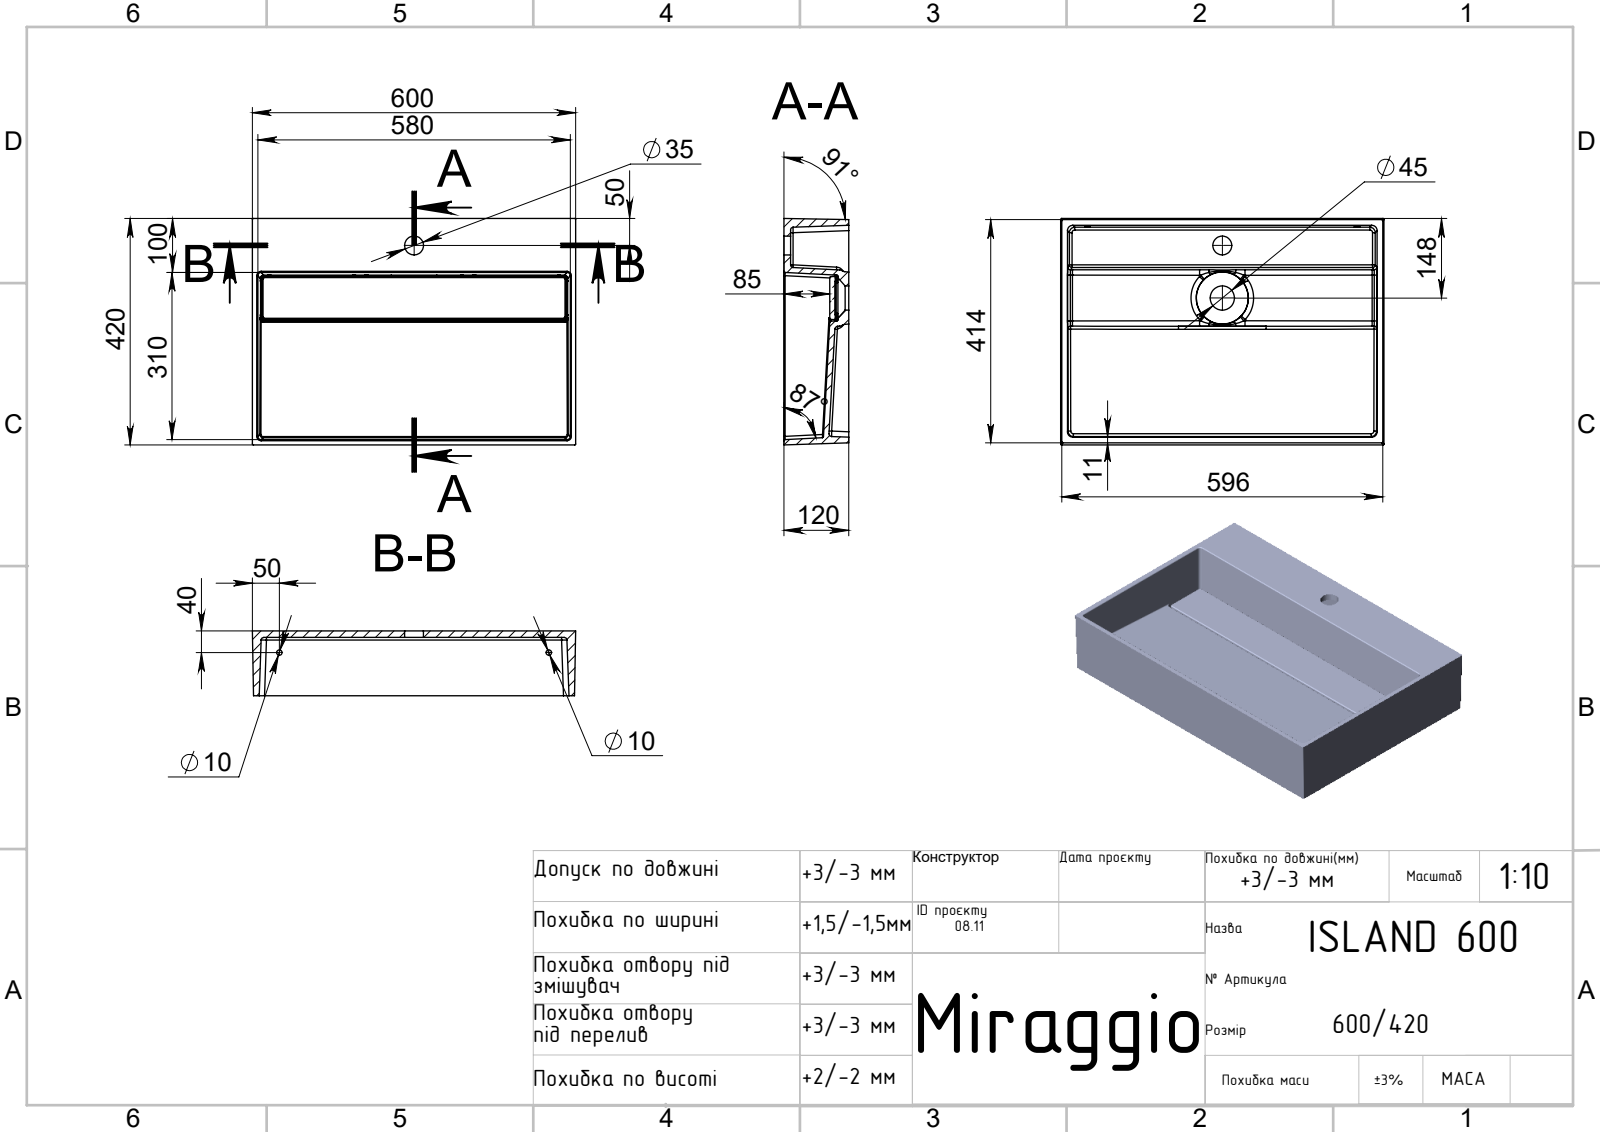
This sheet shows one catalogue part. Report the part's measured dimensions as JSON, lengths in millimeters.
{"part_name": "Logic new 600", "step_written_by": "SolidWorks 2020 (AUTOMOTIVE_DESIGN)", "units": "millimeters", "bodies": {"solids": 2, "faces": 284, "planar": 48, "cylindrical": 88, "other": 148}, "overall_size": [600.19, 420.19, 120], "volume_mm3": 6328000, "surface_area_mm2": 1151000, "round_holes": [[35, 1], [45, 1]], "partial_cylinders_radius": [[2, 24], [10, 12], [5, 11], [6, 7], [1, 4], [4, 4], [7.5, 4]], "face_to_face_distances": [9.99, 10, 95, 10.01, 85, 12, 83, 73, 25, 35], "hole_center_spacings": [97.5]}
